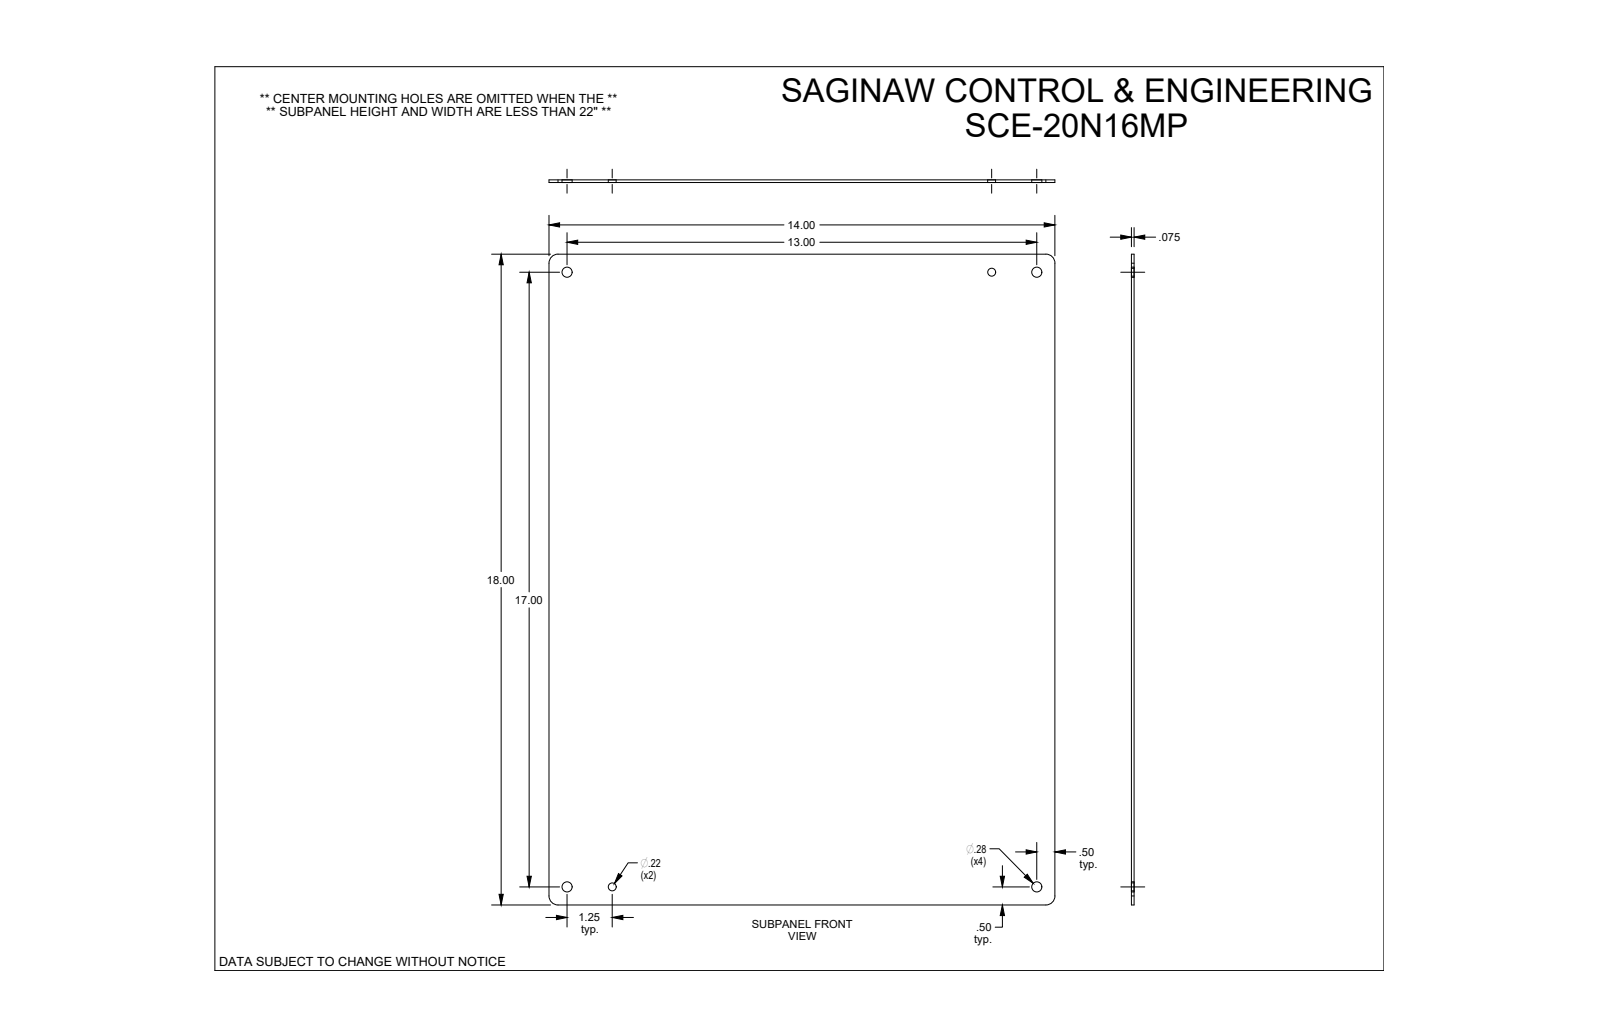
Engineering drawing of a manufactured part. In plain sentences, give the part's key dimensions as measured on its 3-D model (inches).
The part is named "SCE-20N16MP". Its 3-D file was written by "SolidWorks 2019 (CONFIG_CONTROL_DESIGN)". It is 1 solid with 16 faces: 6 planar, 10 cylindrical and 0 other. Overall it measures 18 by 14 by 0.075 inches. Its volume is 18.87 cubic inches and its surface area 508.4 square inches. Round holes: 4 of diameter 0.281, 2 of diameter 0.218. Partial cylindrical surfaces (rounded edges, fillets, slot ends): 4 of radius 0.25. The main face-to-face distances are 0.075, 14, 18. The hole center spacings are 1.25, 11.75, 13, 17, 17.046, 20.665, 21.401, 19.981.
